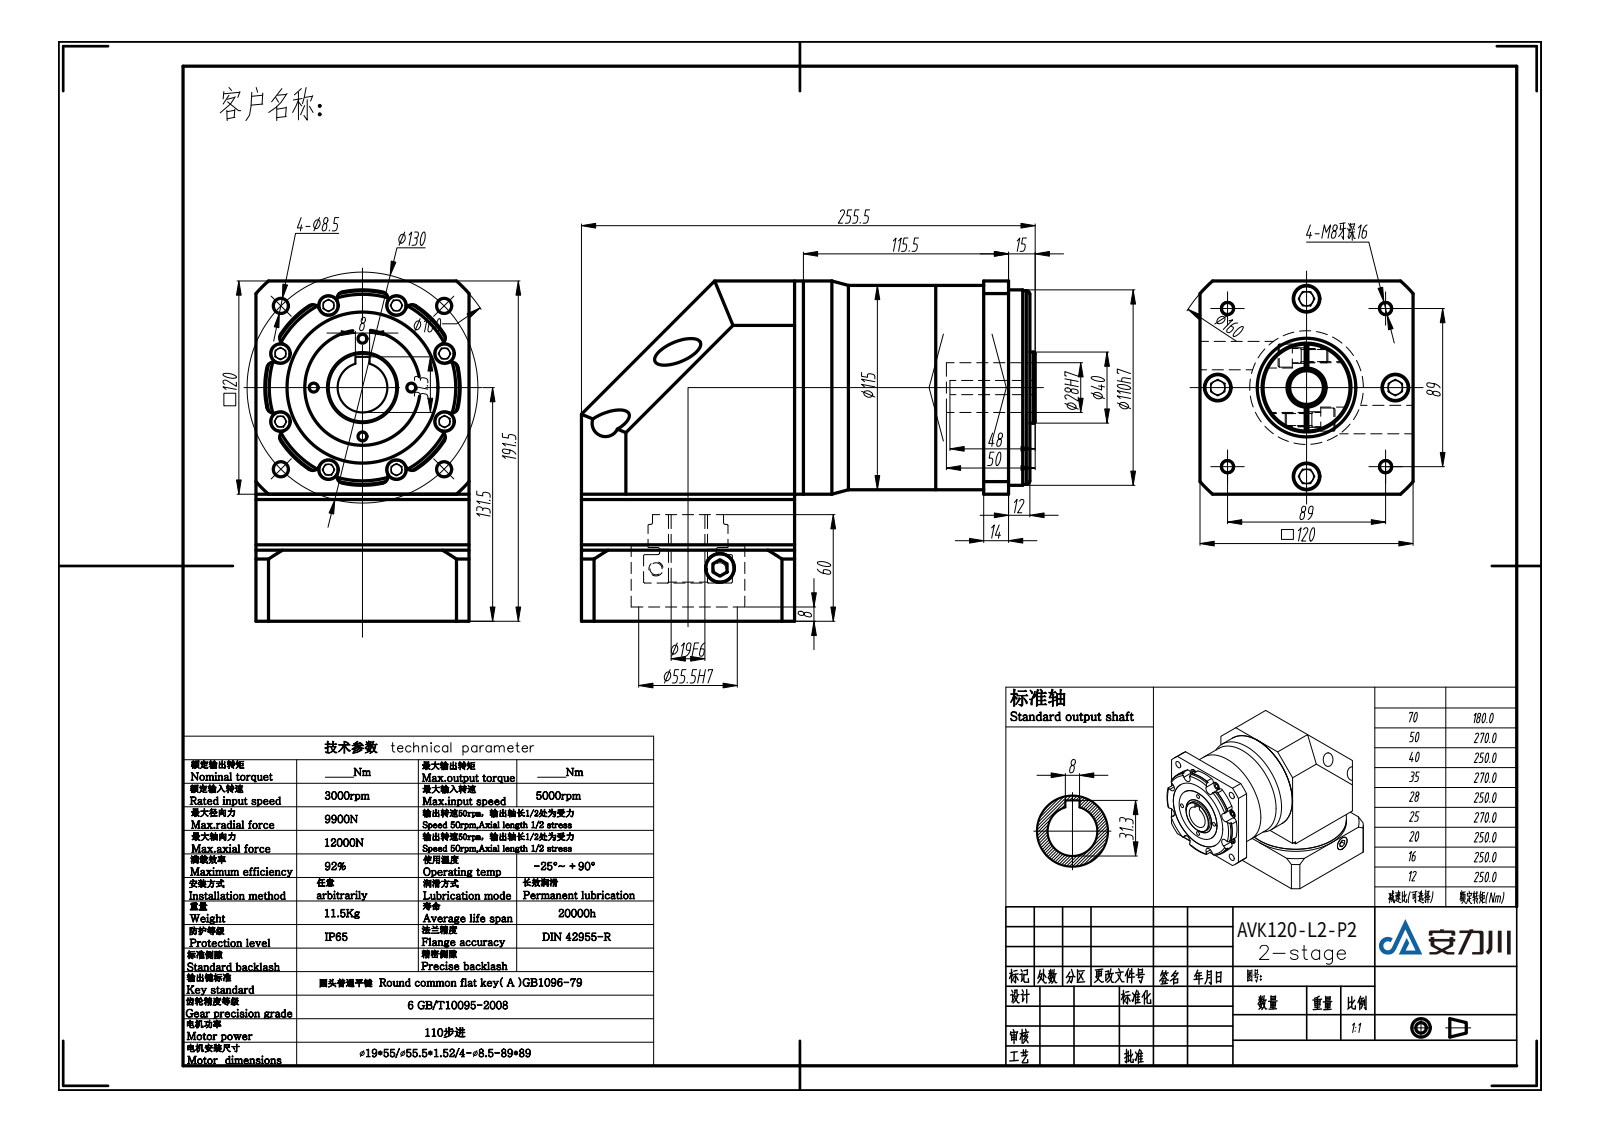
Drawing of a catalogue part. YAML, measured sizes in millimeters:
part_name: "VGZK115双级模型（19-55 55.5-1.52 4-8.5-89-89）"
step_written_by: "SolidWorks 2016 (AUTOMOTIVE_DESIGN)"
units: millimeters
bodies: {solids: 23, faces: 504, planar: 279, cylindrical: 200, other: 25}
overall_size: [255.5, 191.5, 120]
volume: 3416000
surface_area: 355371
round_holes:
  - {diameter: 15, count: 10}
  - {diameter: 11, count: 8}
  - {diameter: 5, count: 4}
  - {diameter: 6.8, count: 4}
  - {diameter: 8.5, count: 4}
  - {diameter: 16, count: 2}
  - {diameter: 19, count: 1}
  - {diameter: 20, count: 1}
  - {diameter: 22, count: 1}
  - {diameter: 28, count: 1}
  - {diameter: 45.2, count: 1}
  - {diameter: 55.5, count: 1}
round_bosses_or_shafts:
  - {diameter: 13, count: 10}
  - {diameter: 9.5, count: 8}
  - {diameter: 120, count: 2}
  - {diameter: 15.6, count: 2}
  - {diameter: 115, count: 1}
  - {diameter: 65, count: 1}
  - {diameter: 50, count: 1}
  - {diameter: 45, count: 1}
partial_cylinders:
  - {radius: 4, count: 16}
  - {radius: 80, count: 2}
  - {radius: 54.5, count: 1}
  - {radius: 55, count: 1}
face_to_face_distances: [5, 120, 25.5, 49.17, 74.5, 79.5, 25.33, 30.33, 43, 68.5]
hole_center_spacings: [39.29, 94.69, 26.74, 26.83, 44.84, 46.94, 49.53, 49.99]
